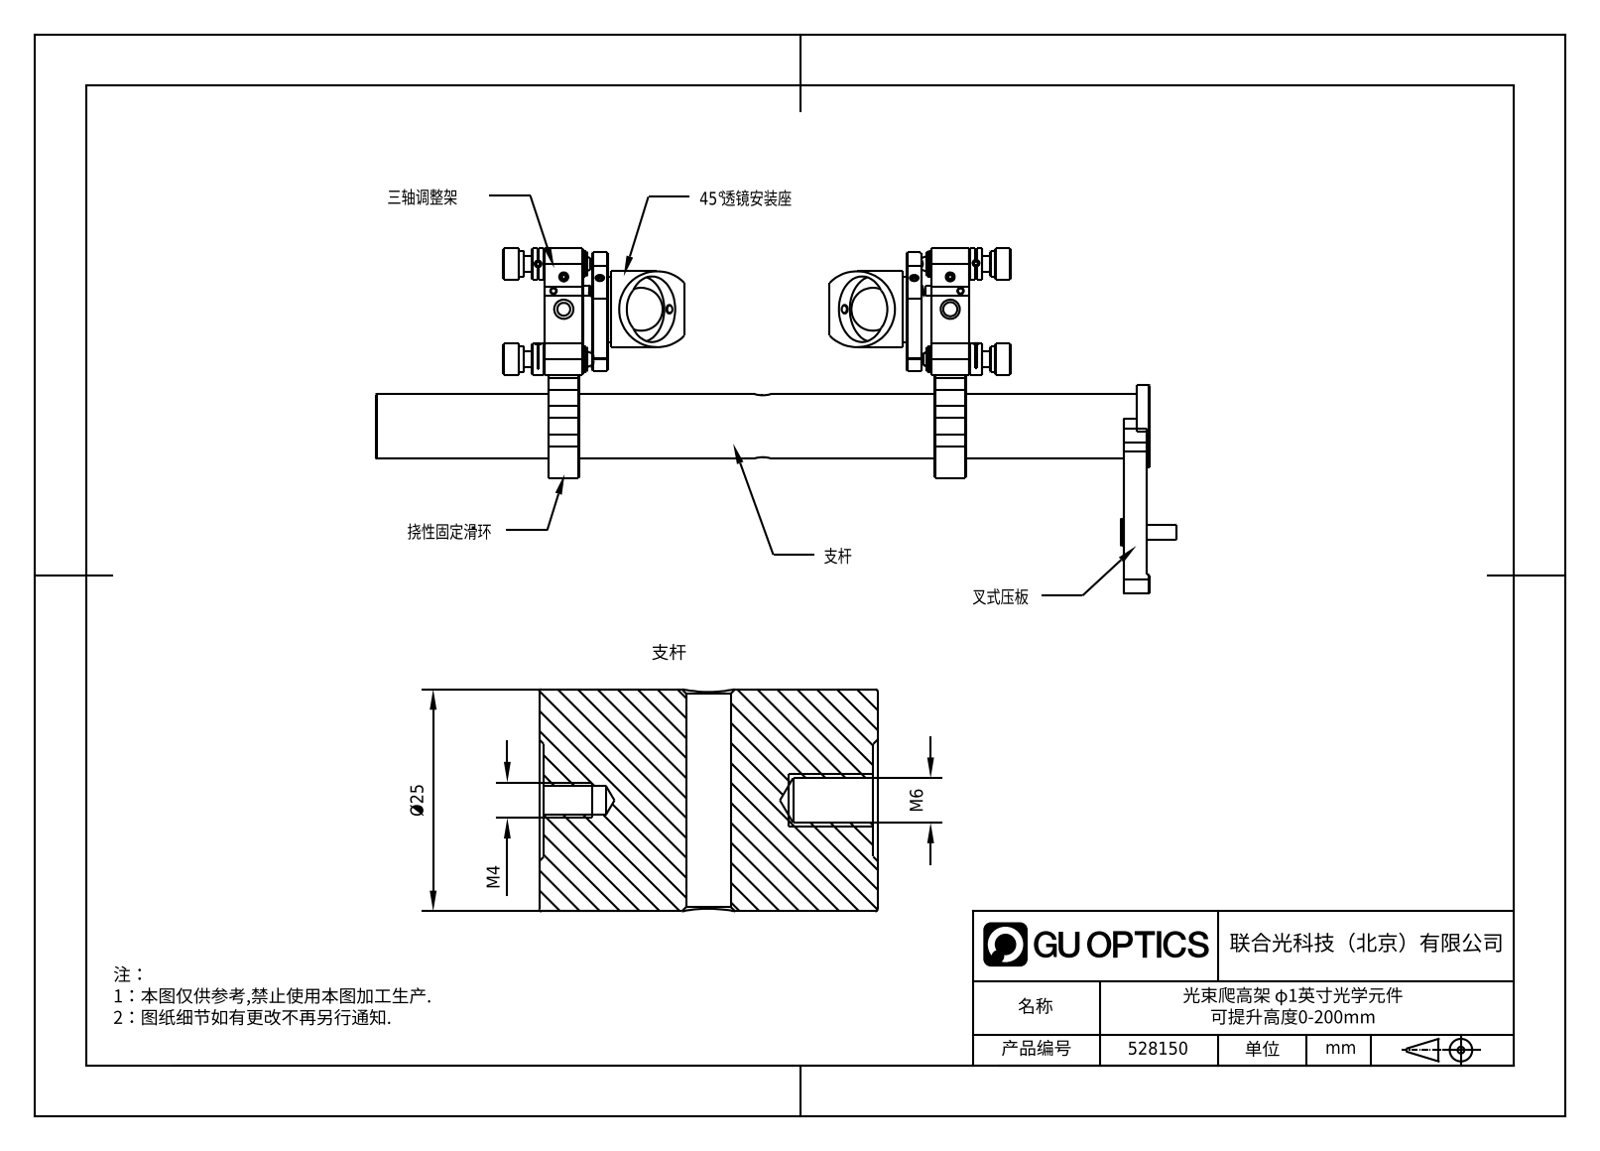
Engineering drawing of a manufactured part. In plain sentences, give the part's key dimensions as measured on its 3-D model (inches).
The part is named "528150". Its 3-D file was written by "SolidWorks 2020 (CONFIG_CONTROL_DESIGN)". It is 0 solids with 847 faces: 371 planar, 187 cylindrical and 289 other. Overall it measures 12.224 by 5.276 by 1.931 inches. Round holes: 7 of diameter 0.157, 4 of diameter 0.098, 4 of diameter 0.295, 3 of diameter 0.197, 2 of diameter 0.13, 2 of diameter 0.236, 2 of diameter 0.656, 2 of diameter 1.003, 1 of diameter 0.217, 1 of diameter 0.374, 1 of diameter 0.492, 1 of diameter 0.5. Round bosses or shafts: 8 of diameter 0.118, 4 of diameter 0.236, 4 of diameter 0.157, 3 of diameter 0.472, 3 of diameter 0.394, 3 of diameter 0.315, 2 of diameter 0.374, 2 of diameter 0.283. Partial cylindrical surfaces (rounded edges, fillets, slot ends): 6 of radius 0.079, 6 of radius 0.157, 6 of radius 0.197, 4 of radius 0.039, 3 of radius 0.177, 3 of radius 0.236, 3 of radius 0.591, 2 of radius 0.008. The main face-to-face distances are 0.059, 0.236, 0.197, 5.906, 0.531, 4.803, 5, 0.472, 3.316, 0.433. The hole center spacings are 0.321, 6.069, 0.413, 0.813, 1.031, 1.043, 1.457, 1.792.
